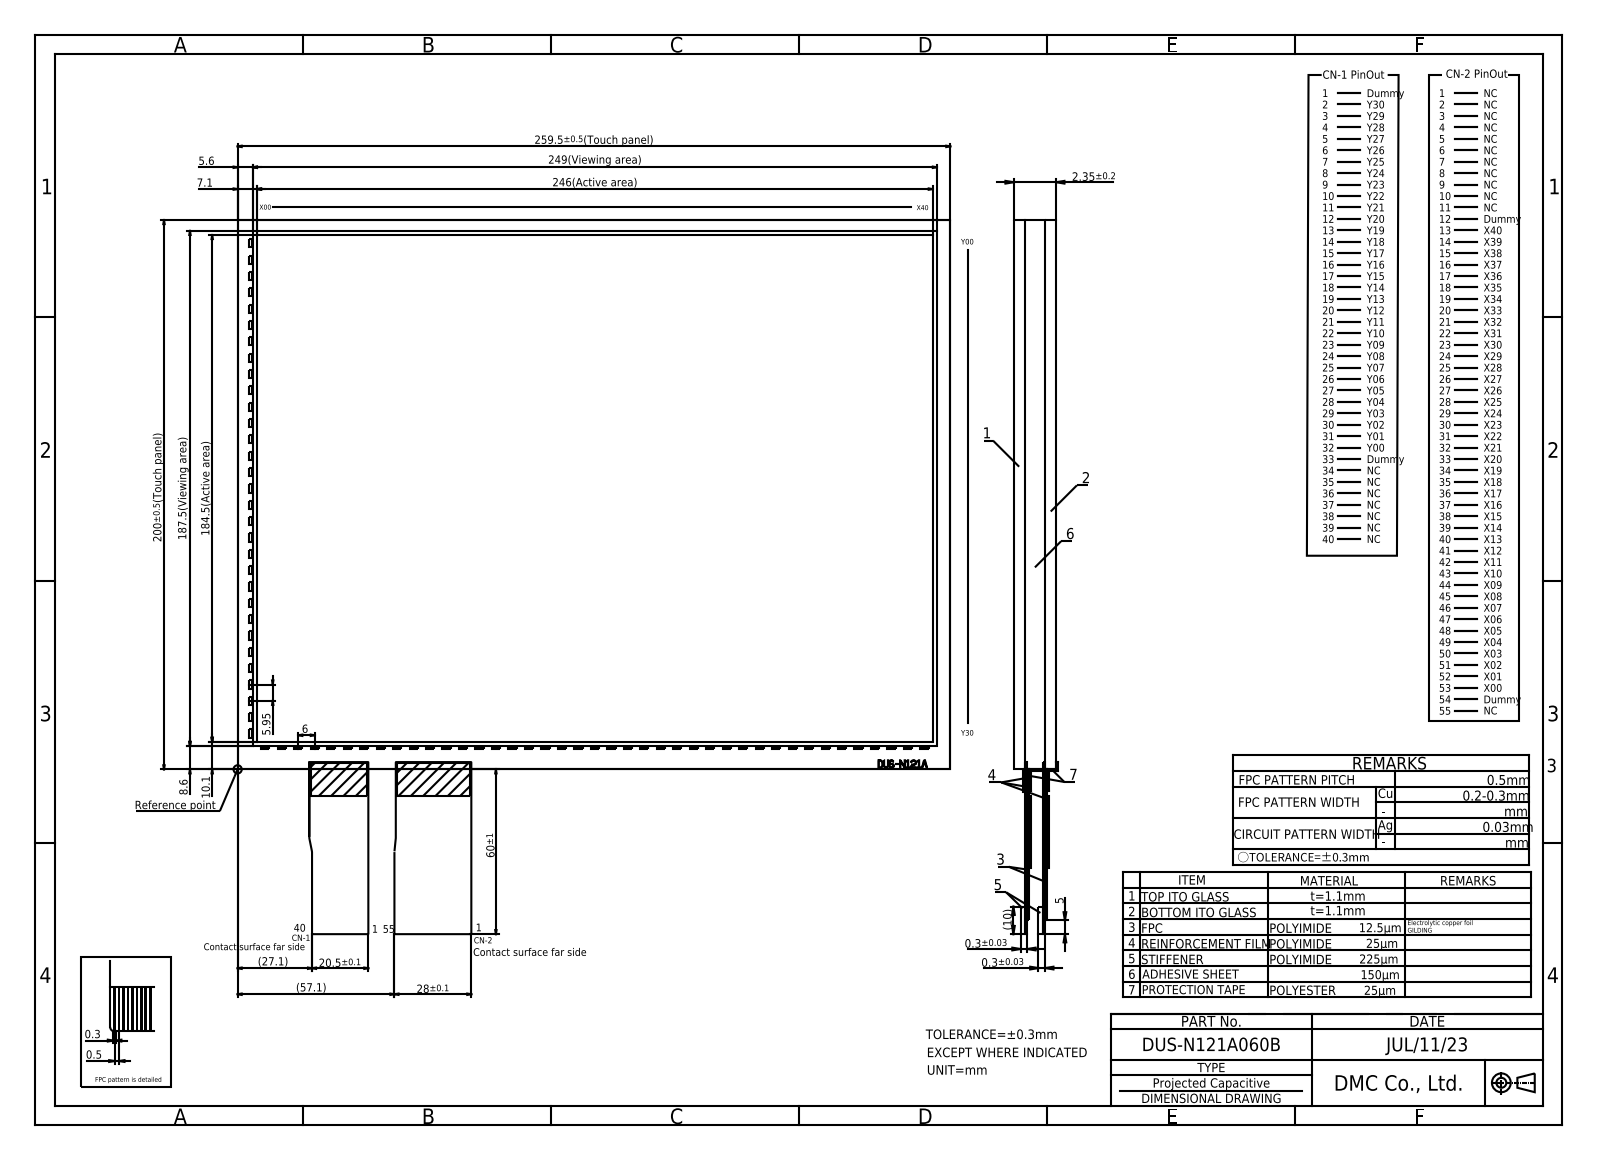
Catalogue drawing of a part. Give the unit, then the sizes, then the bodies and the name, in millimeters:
Units: millimetres
Overall size (bounding box): 363.3 × 300 × 2.35
Partial cylindrical surfaces — rounded edges, fillets, slot ends (radius × count): R0.2 ×4, R5 ×2
Main face-to-face distances: 2.35, 1.12, 1.23, 1.25, 1.1, 1, 2.25, 1.13, 200, 0.8
Volume: 122 322 mm³ · Surface area: 112 085 mm²
Bodies: 1 solid, 422 faces (416 planar, 6 cylindrical, 0 other)
Part name (STEP PRODUCT): DUS-N121A060B
STEP written by: Autodesk Inventor 2020 (CONFIG_CONTROL_DESIGN)
